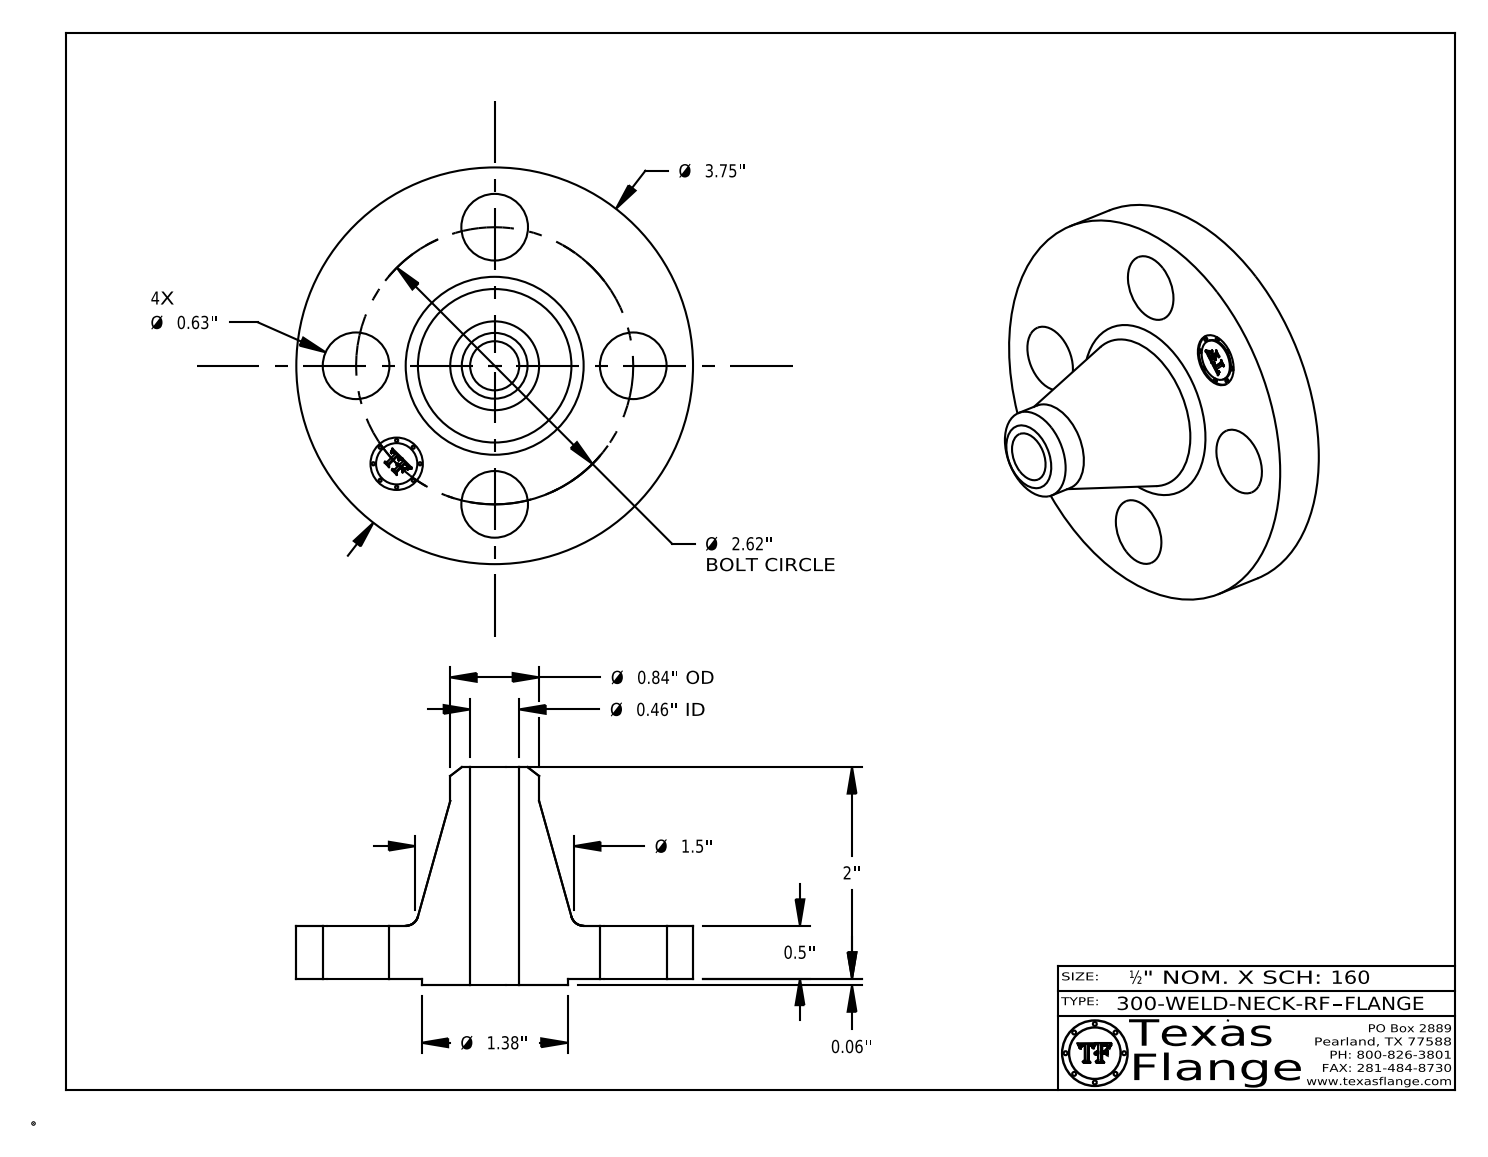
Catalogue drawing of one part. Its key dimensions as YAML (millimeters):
part_name: "300-WELD-NECK-RF"
step_written_by: "CATIA V5 STEP AP214 (AUTOMOTIVE_DESIGN)"
units: millimeters
bodies: {solids: 1, faces: 411, planar: 369, cylindrical: 36, other: 6}
overall_size: [95.3, 95.3, 52.4]
volume: 100300
surface_area: 23450
round_holes:
  - {diameter: 16, count: 4}
  - {diameter: 11.8, count: 1}
  - {diameter: 12.6, count: 1}
round_bosses_or_shafts:
  - {diameter: 0.8, count: 8}
  - {diameter: 95.3, count: 1}
  - {diameter: 35.1, count: 1}
  - {diameter: 21.3, count: 1}
  - {diameter: 9.9, count: 1}
face_to_face_distances: [12.7, 1.6, 14.3, 52.4, 50.8, 38.1, 13.9, 12.3, 0.4, 38.5]
hole_center_spacings: [33.3, 47, 25.5, 61.5, 66.5, 33.3]
